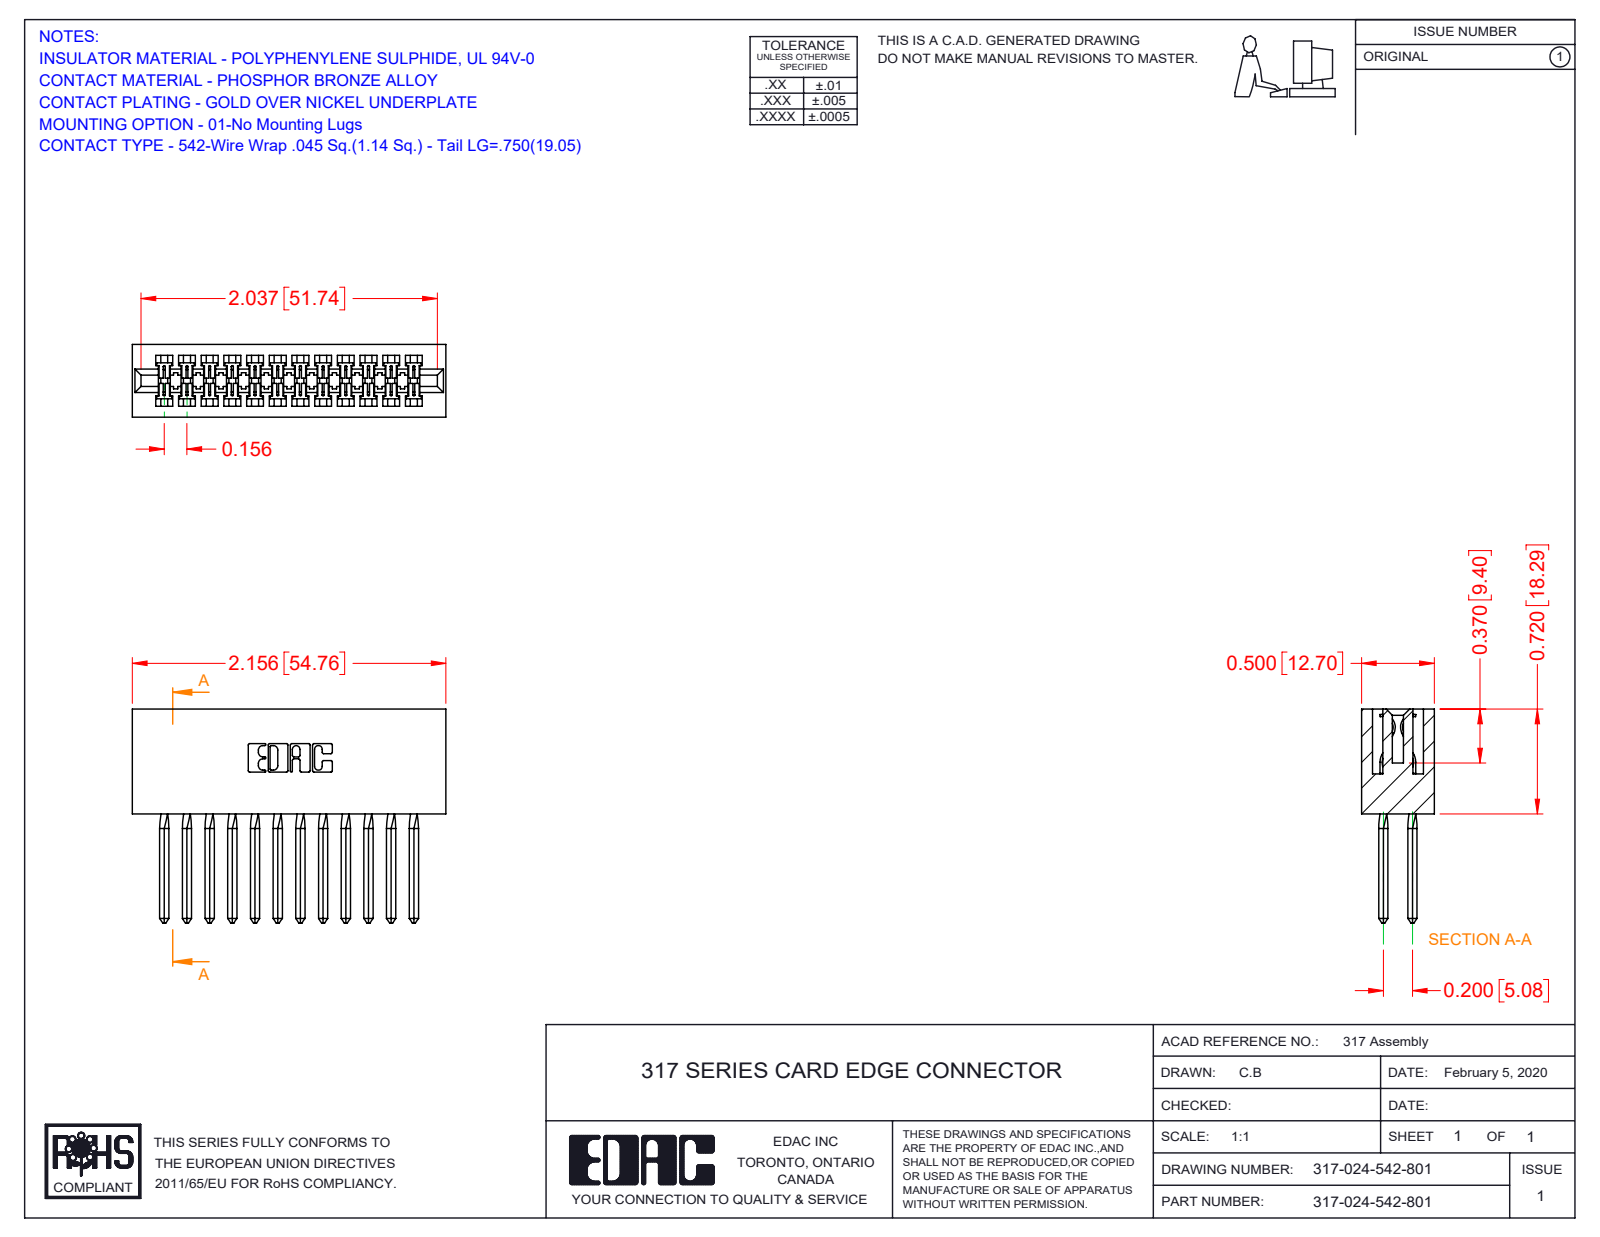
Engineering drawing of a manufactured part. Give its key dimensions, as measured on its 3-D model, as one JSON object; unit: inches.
{"part_name": "317-290-003_542; 317-024-542-801; 317 Part_Lugless", "step_written_by": "SolidWorks 2016 (CONFIG_CONTROL_DESIGN)", "units": "inches", "bodies": {"solids": 25, "faces": 1458, "planar": 1154, "cylindrical": 208, "other": 96}, "overall_size": [2.156, 1.47, 0.5], "volume_in3": 0.595, "surface_area_in2": 19.8, "partial_cylinders_radius": [[0.006, 48], [0.01, 22], [0.007, 6], [0.031, 6], [0.026, 3], [0.074, 2], [0.089, 2], [0.1, 2]], "face_to_face_distances": [0.5, 0.075, 0.425, 0.11, 0.116, 0.156, 0.35, 0.22, 0.2, 0.136]}
